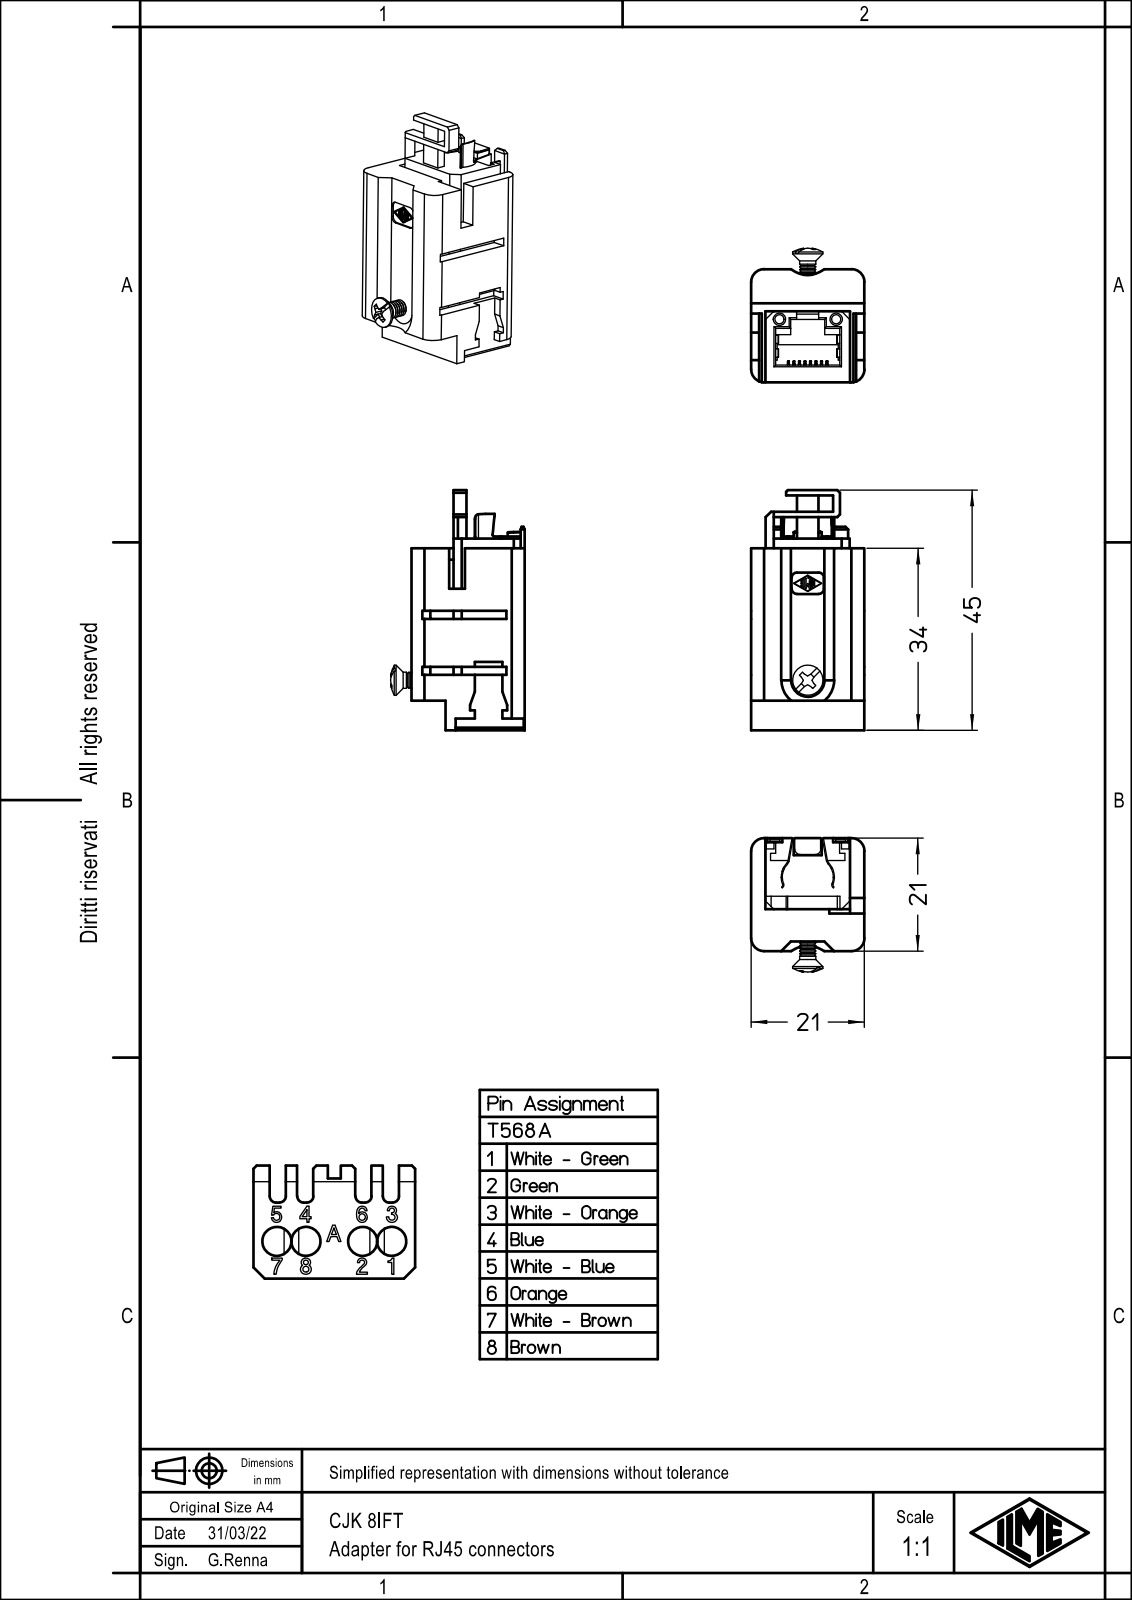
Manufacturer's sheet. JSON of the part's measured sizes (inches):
{"part_name": "CJK_8IFT", "step_written_by": "PTC Creo Elements/Direct Modeling 19.0E 27-Jun-2016 (C) Parametric Technology GmbH (AUTOMOTIVE_DESIGN)", "units": "inches", "bodies": {"solids": 1, "faces": 589, "planar": 376, "cylindrical": 139, "other": 74}, "overall_size": [1.756, 0.98, 0.827], "volume_in3": 0.647, "surface_area_in2": 12.68, "round_holes": [[0.067, 2]], "round_bosses_or_shafts": [[0.22, 1], [0.118, 1]], "partial_cylinders_radius": [[0.004, 63], [0.039, 10], [0.012, 8], [0.031, 4], [0.094, 4], [0.138, 3], [0.016, 2], [0.024, 2]], "face_to_face_distances": [0.106, 0.616, 0.72, 0.104, 0.722, 0.059, 0.618, 0.614, 0.827, 0.519], "hole_center_spacings": [0.413]}
